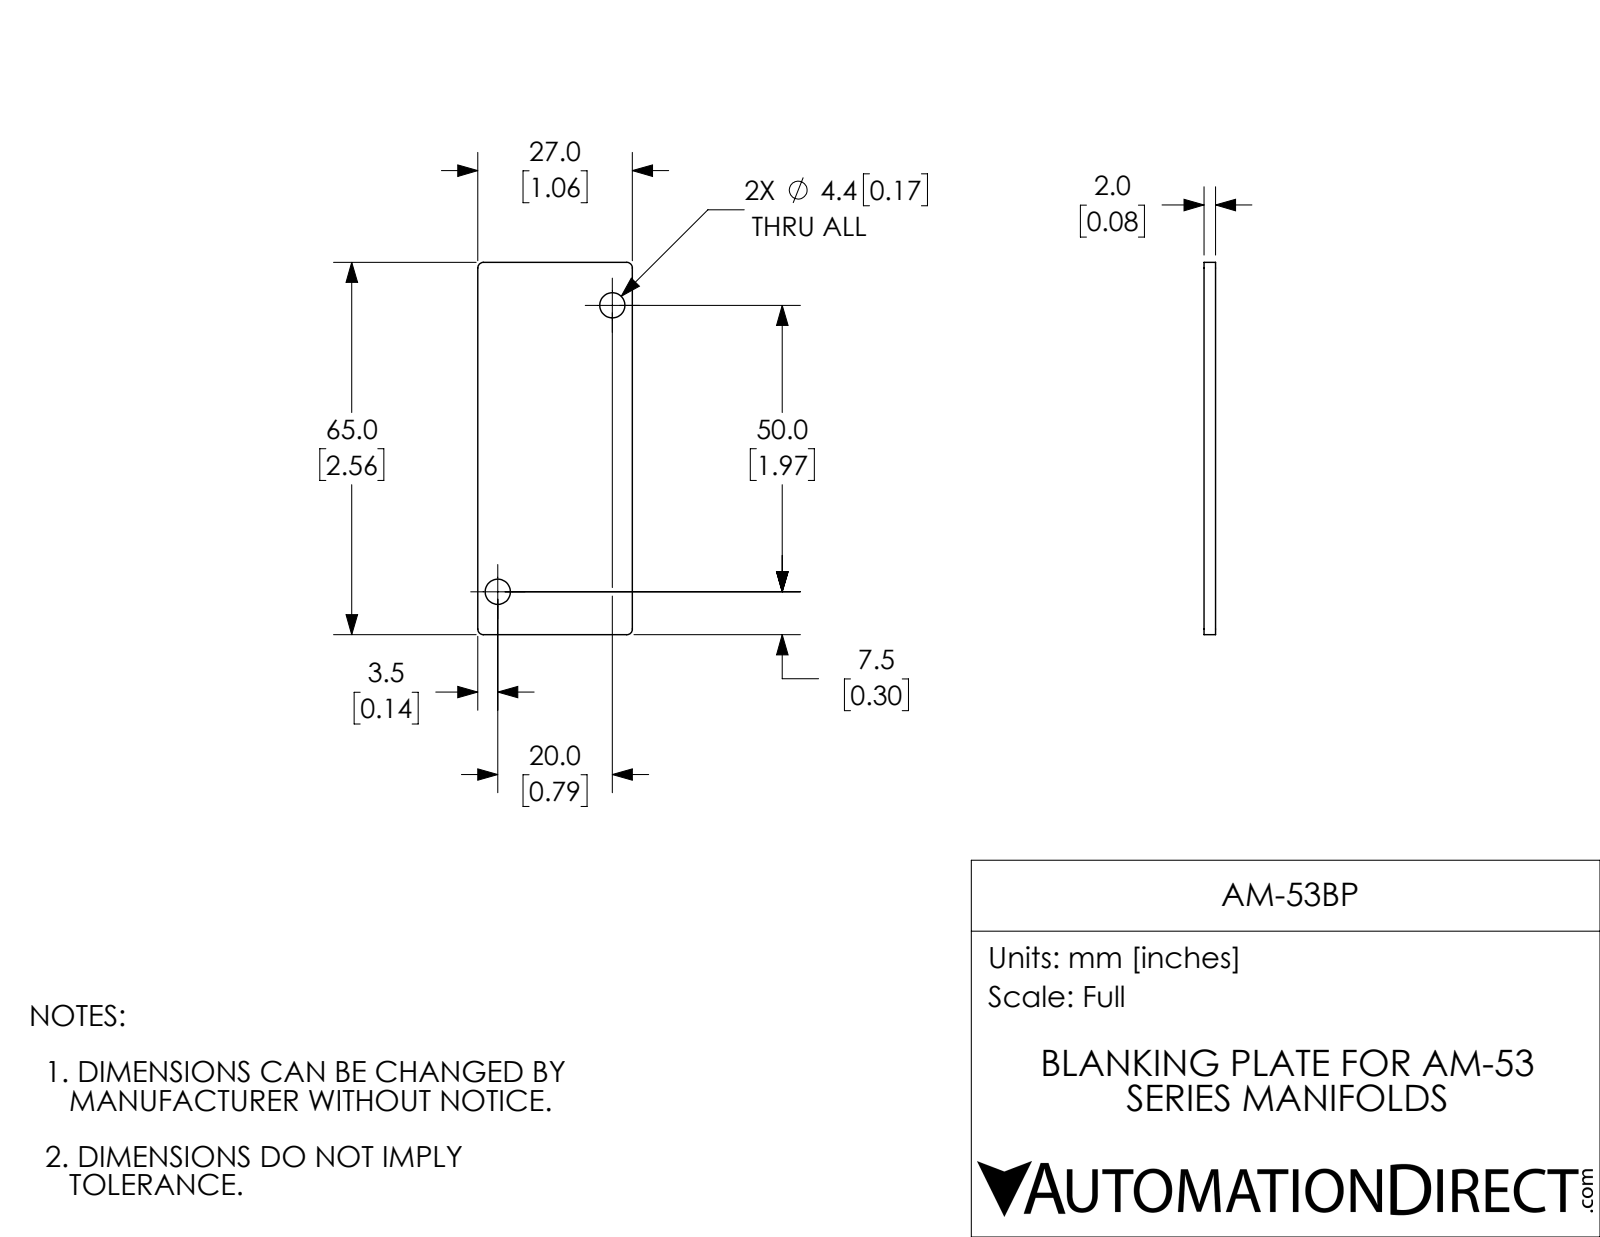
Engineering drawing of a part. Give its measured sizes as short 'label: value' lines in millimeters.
name: AM-53BP
written by: SolidWorks 2017 (AUTOMOTIVE_DESIGN)
unit: mm
bodies: 1 solid, 14 faces (6 planar, 8 cylindrical, 0 other)
size: 65 × 27 × 2
volume: 3 447 mm³; area: 3 867 mm²
holes: 2× ⌀4.4
rounds: 4× R1
face distances: 2, 27, 65
hole spacings: 53.85
